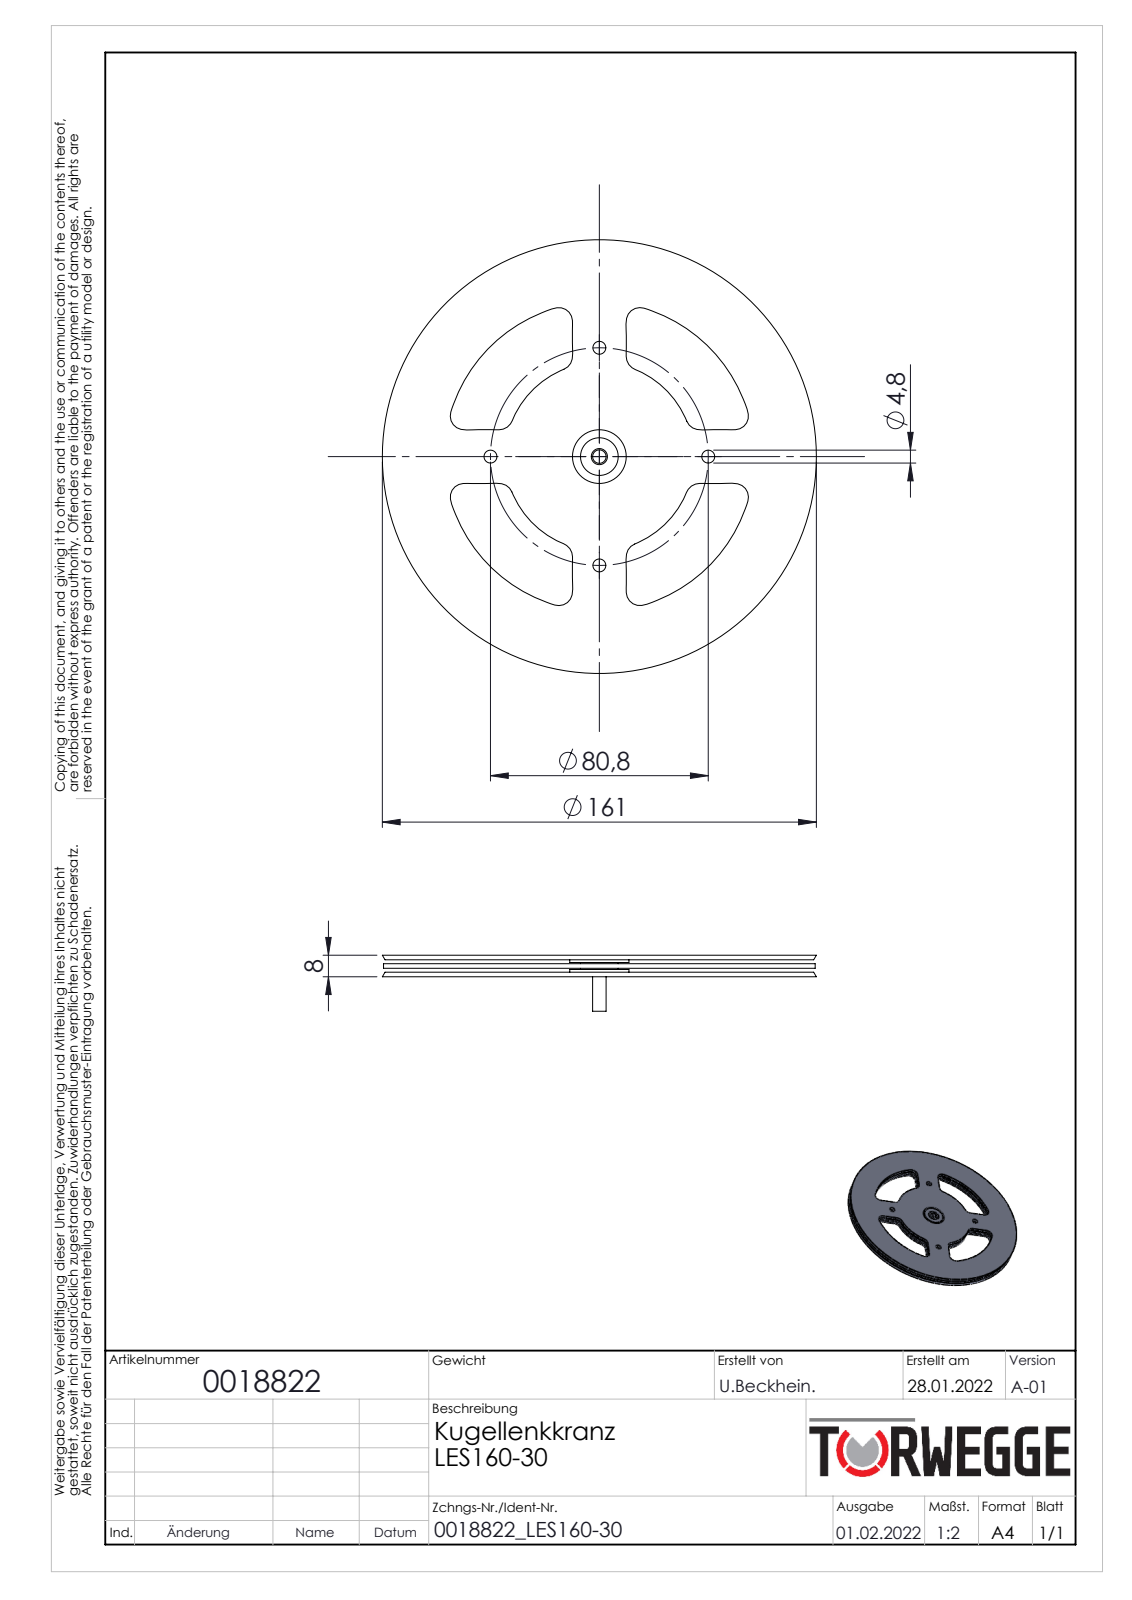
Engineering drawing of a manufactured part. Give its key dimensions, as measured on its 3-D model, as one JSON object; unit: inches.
{"part_name": "0018822", "step_written_by": "SolidWorks 2020 (AUTOMOTIVE_DESIGN)", "units": "inches", "bodies": {"solids": 2, "faces": 107, "planar": 25, "cylindrical": 54, "other": 28}, "overall_size": [6.34, 6.34, 0.819], "volume_in3": 4.826, "surface_area_in2": 153.8, "round_holes": [[0.189, 4], [0.236, 1], [0.394, 1], [0.785, 1], [0.864, 1]], "round_bosses_or_shafts": [[6.305, 1], [0.709, 1], [0.551, 1], [0.354, 1], [0.197, 1]], "face_to_face_distances": [0.124, 0.067, 0.191, 0.248, 0.057, 0.315, 0.181, 0.071, 0.039, 0.138], "hole_center_spacings": [1.591, 2.249, 3.181]}
